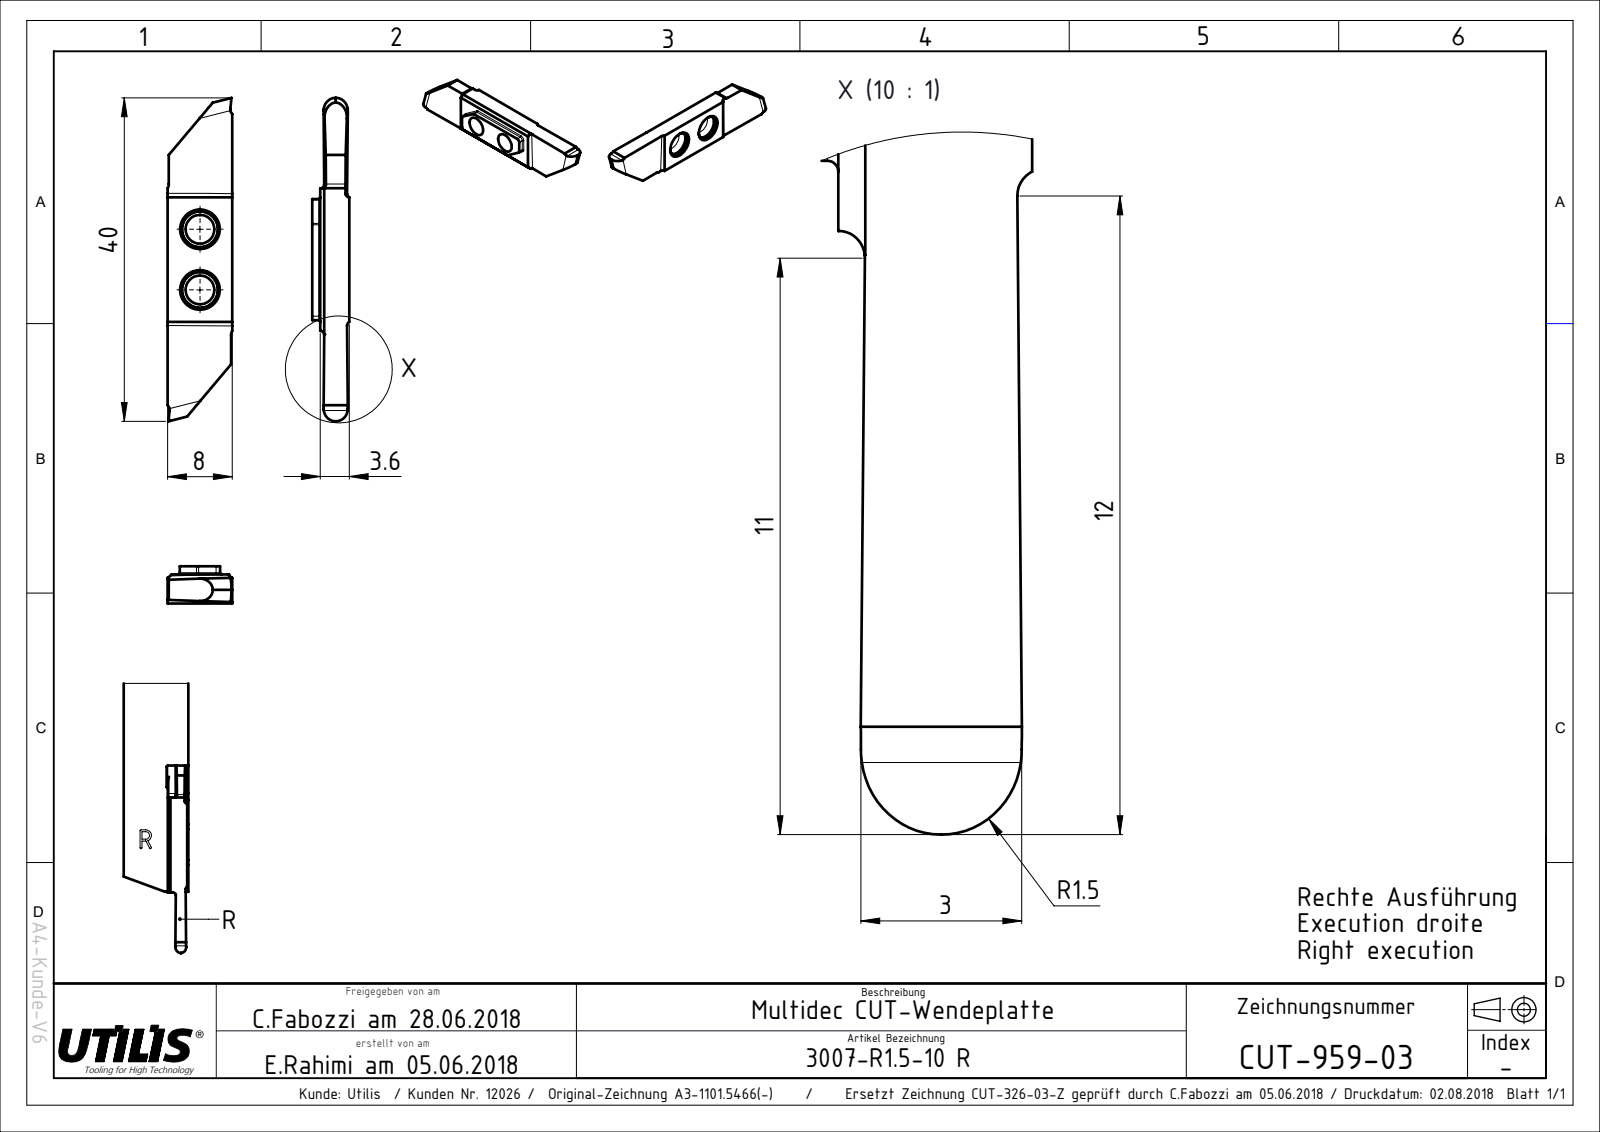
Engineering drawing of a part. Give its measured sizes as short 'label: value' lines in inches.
name: CUT-959; ASME Y14.5
written by: FormatWorks Professional (AP242_MANAGED_MODEL_BASED_3D_ENGINEERING_MIM_LF)
unit: in
bodies: 1 solid, 38 faces (20 planar, 16 cylindrical, 2 other)
size: 1.575 × 0.315 × 0.142
volume: 0.048 in³; area: 1.32 in²
holes: 2× ⌀0.14
rounds: 4× R0.059, 2× R0.02, 2× R0.031, 2× R0.039
face distances: 0.142, 0.315, 0.097, 0.097, 0.887, 0.309, 0.303, 0.283, 0.693, 0.018
hole spacings: 0.295
